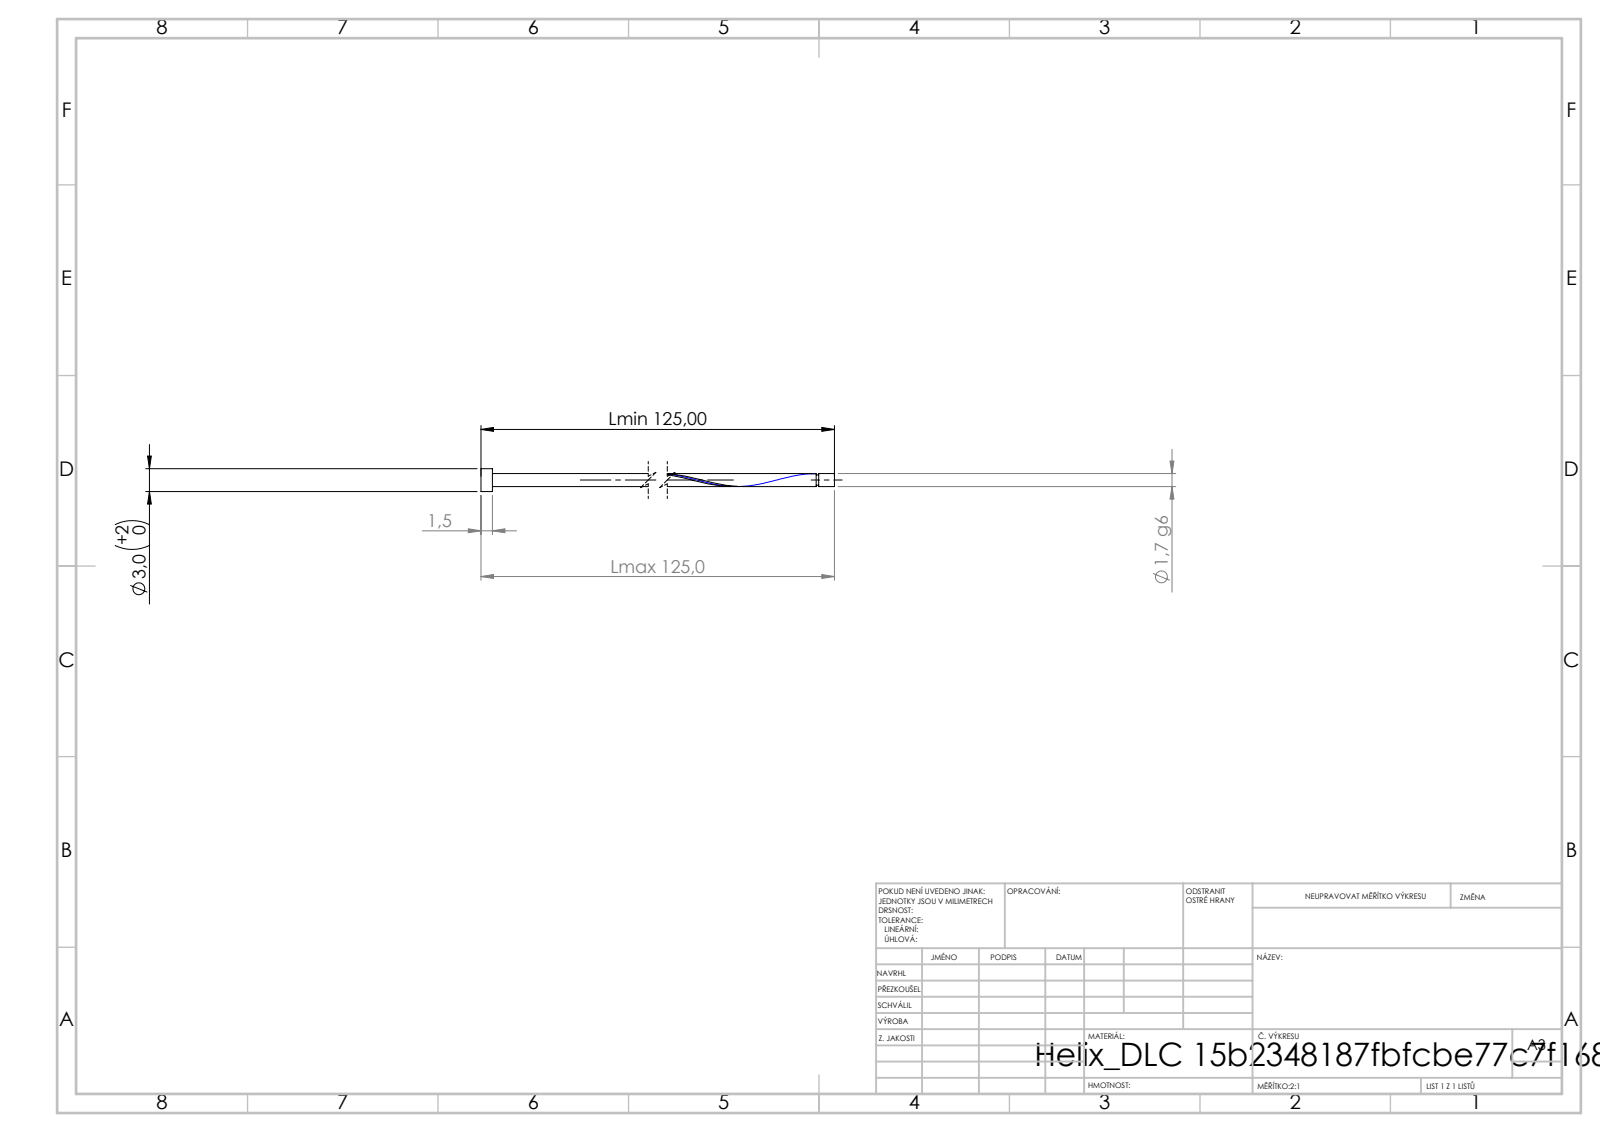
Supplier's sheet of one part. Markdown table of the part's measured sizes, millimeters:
| quantity | value |
| --- | --- |
| STEP written by | SolidWorks 2019 (CONFIG_CONTROL_DESIGN) |
| units | millimeters |
| bodies | 1 solid, 16 faces (6 planar, 9 cylindrical, 1 other) |
| overall size | 125 × 3 × 3 |
| volume | 351 mm³ |
| surface area | 923 mm² |
| round bosses / shafts (diameter × count) | 3 × 1, 1.7 × 1, 1.36 × 1 |
| main face-to-face distances | 1.5, 125, 123.5, 122.93, 121.43, 2.07, 122.59, 121.09, 0.34, 2.41 |
